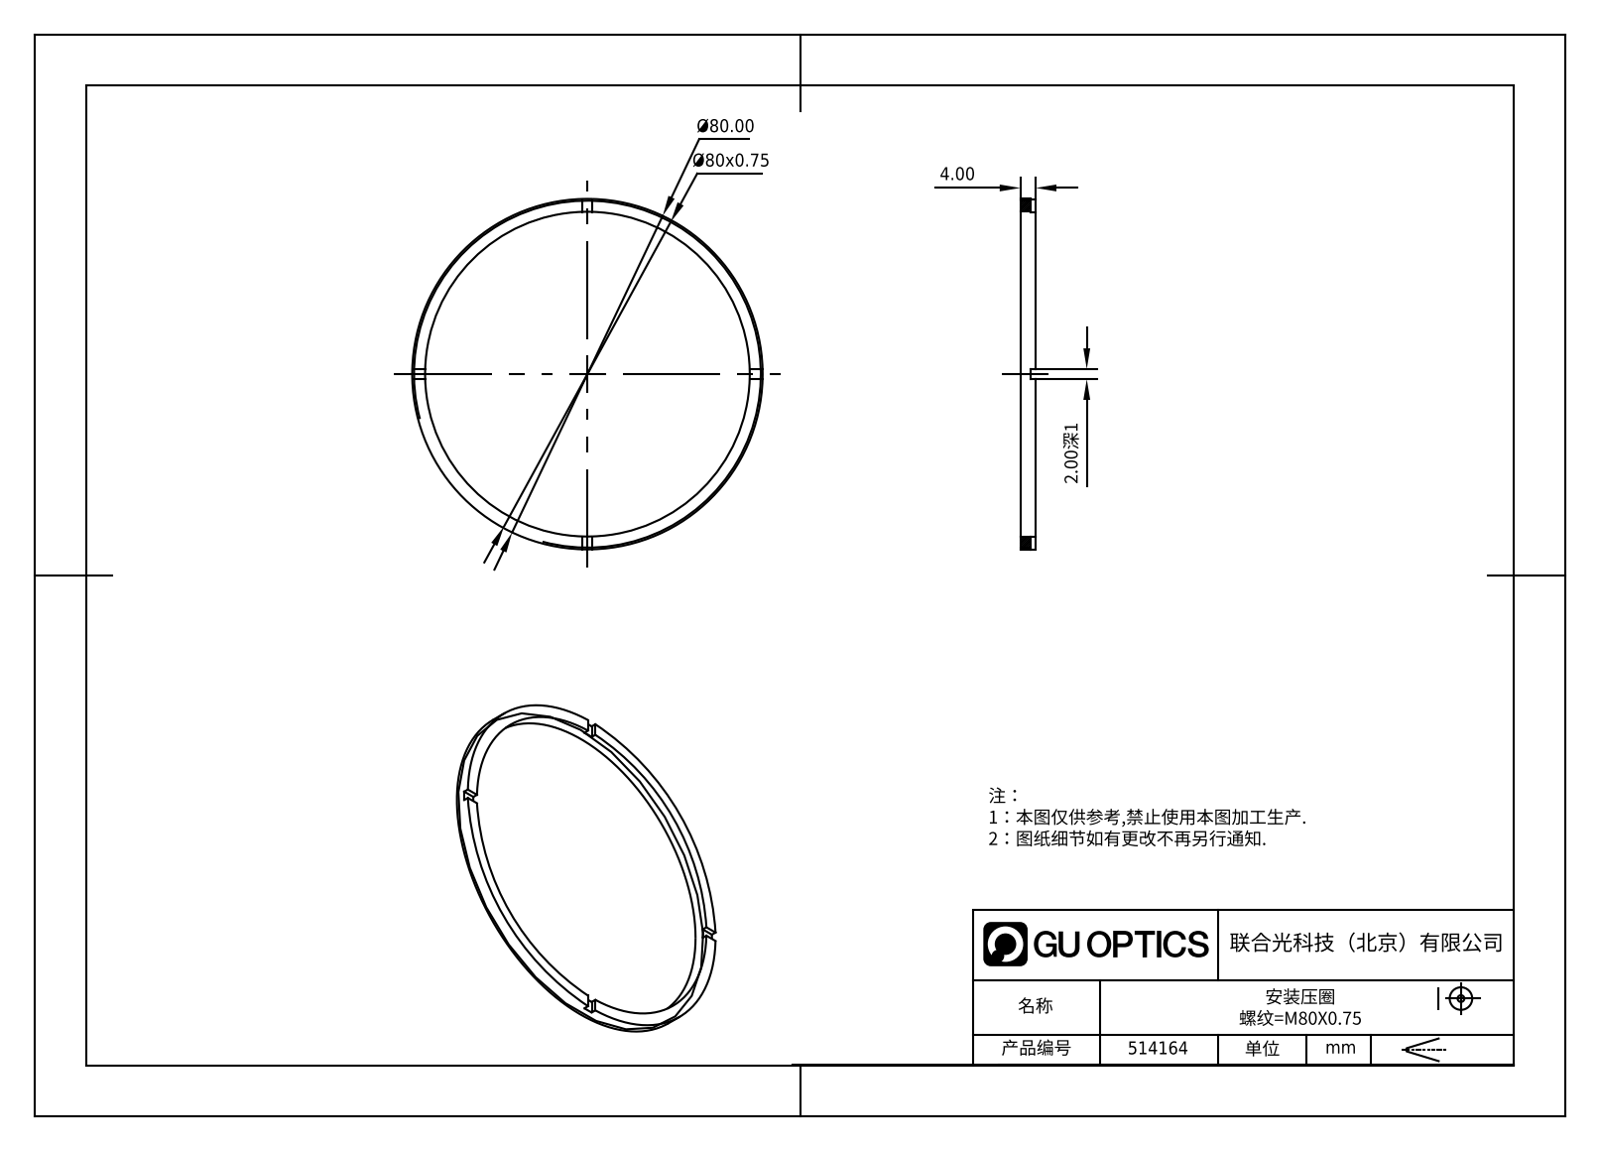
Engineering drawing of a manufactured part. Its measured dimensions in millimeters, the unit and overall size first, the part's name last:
Units: millimetres
Overall size (bounding box): 80 × 80 × 4
Round holes (diameter × count): ⌀74 ×1
Round bosses / shafts (diameter × count): ⌀80 ×1
Main face-to-face distances: 4, 3, 1, 2
Volume: 2 879 mm³ · Surface area: 3 395 mm²
Bodies: 1 solid, 21 faces (17 planar, 4 cylindrical, 0 other)
Part name (STEP PRODUCT): 514164
STEP written by: SolidWorks 2020 (CONFIG_CONTROL_DESIGN)
